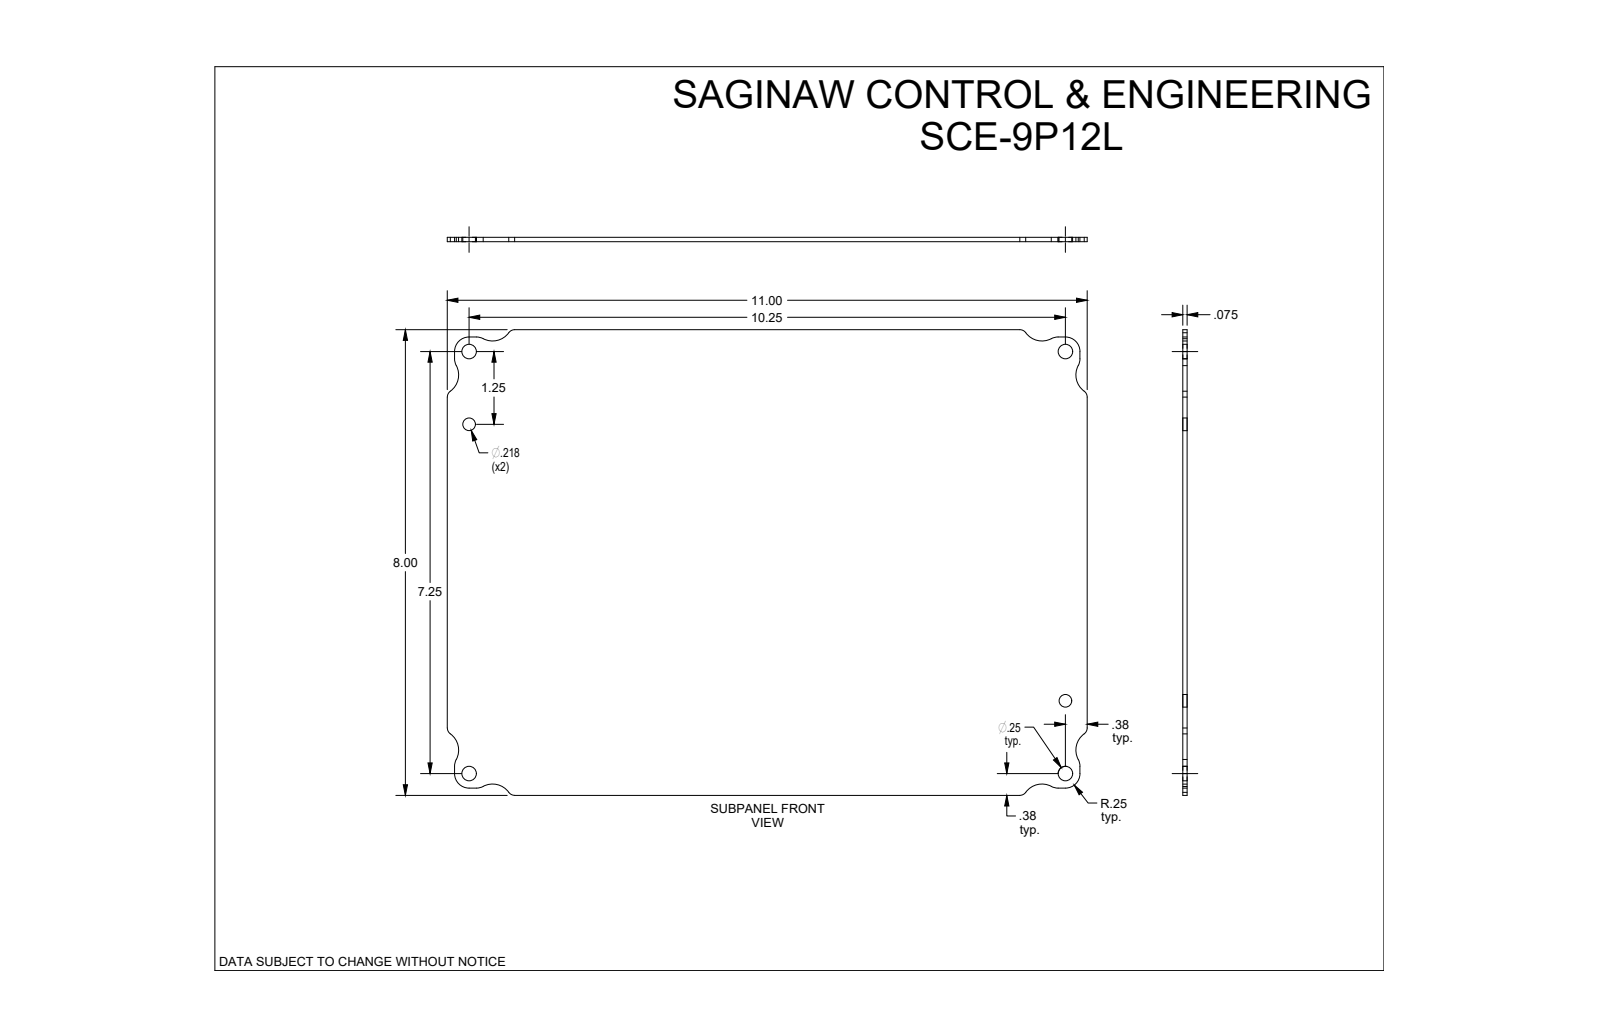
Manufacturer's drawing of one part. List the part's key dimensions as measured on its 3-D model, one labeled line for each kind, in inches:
Part name (STEP PRODUCT): SCE-9P12L
STEP written by: SolidWorks 2019 (CONFIG_CONTROL_DESIGN)
Units: inches
Bodies: 1 solid, 48 faces (14 planar, 34 cylindrical, 0 other)
Overall size (bounding box): 11 × 8 × 0.075
Volume: 6.49 in³ · Surface area: 176.2 in²
Round holes (diameter × count): ⌀0.25 ×4, ⌀0.218 ×2
Partial cylindrical surfaces — rounded edges, fillets, slot ends (radius × count): R0.25 ×12, R0.125 ×8, R0.344 ×8
Main face-to-face distances: 0.075, 8, 11, 0.125, 10.875, 0.125, 7.875, 10.75, 7.75
Hole centre spacings: 1.25, 6, 7.25, 10.25, 10.326, 11.876, 12.554, 11.296
